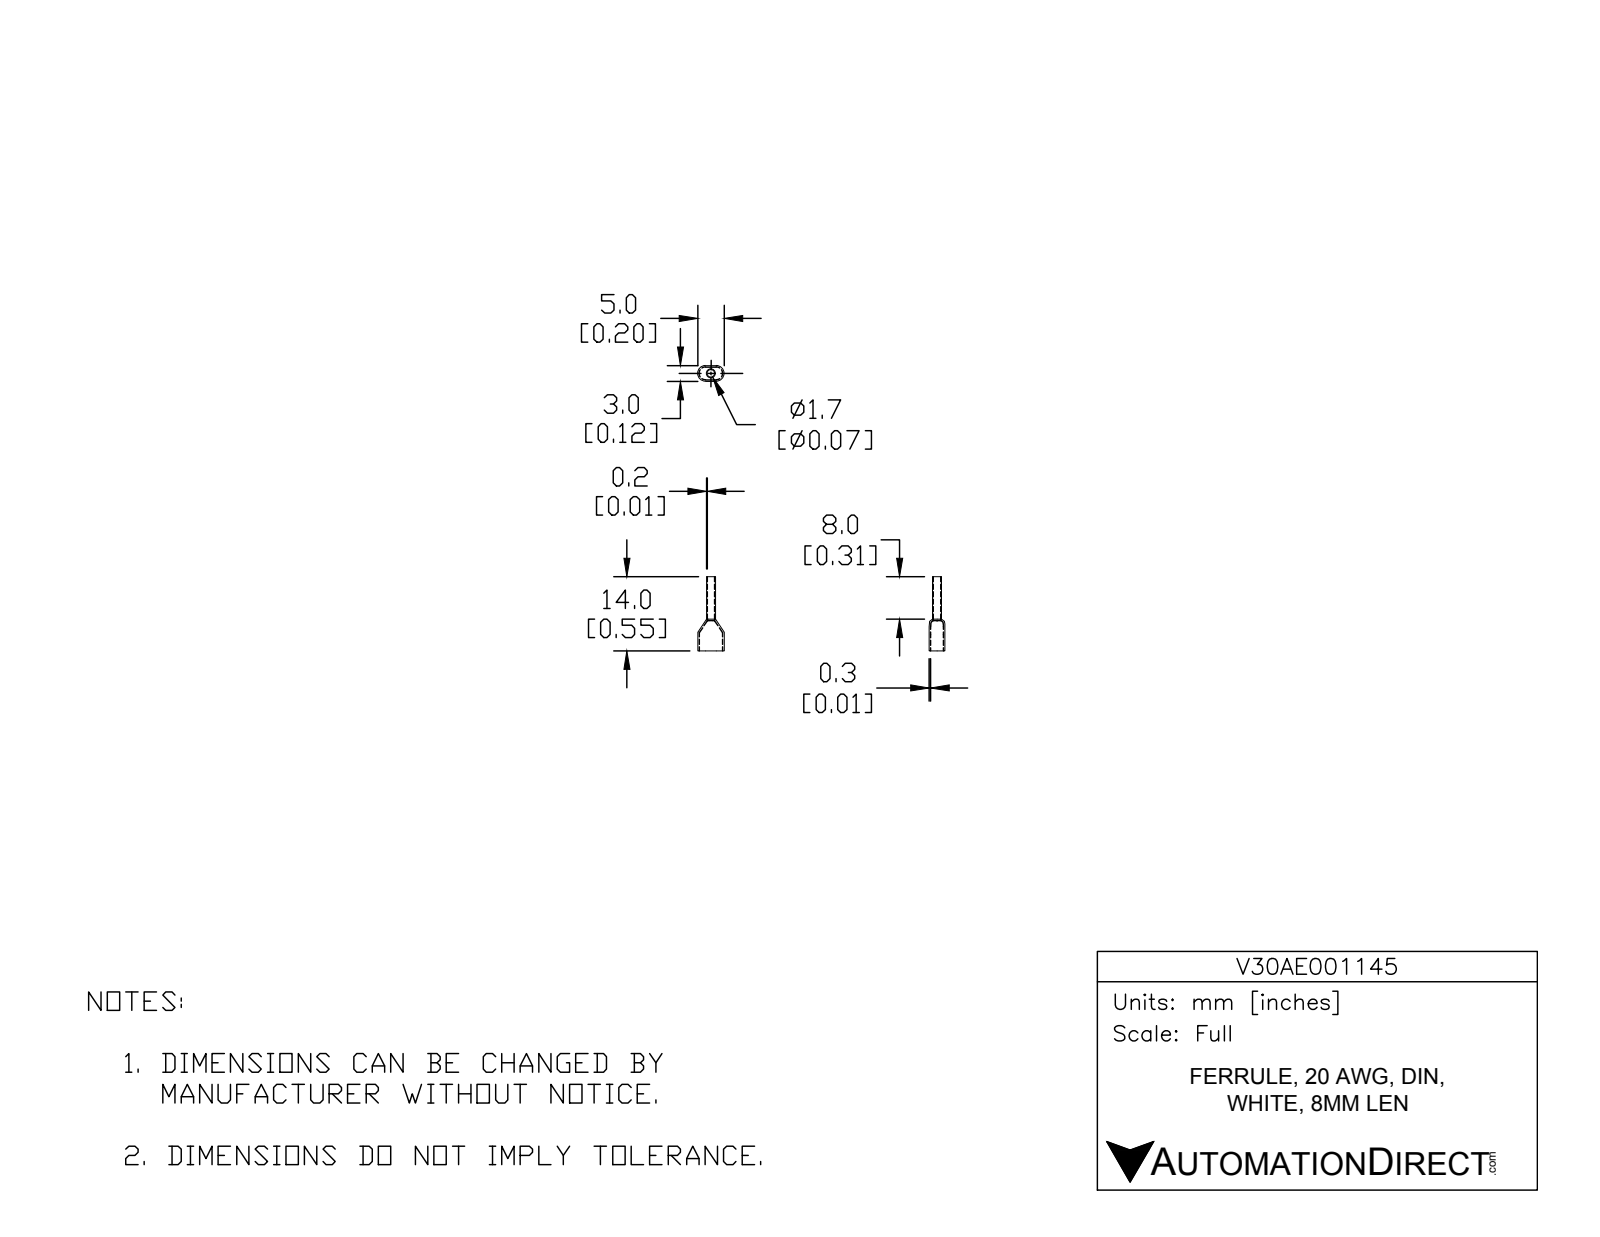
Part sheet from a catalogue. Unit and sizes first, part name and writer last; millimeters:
Units: millimetres
Overall size (bounding box): 14 × 5 × 3
Round holes (diameter × count): ⌀1.4 ×1
Round bosses / shafts (diameter × count): ⌀1.7 ×1
Partial cylindrical surfaces — rounded edges, fillets, slot ends (radius × count): R1.2 ×6, R1.5 ×6
Main face-to-face distances: 2.7, 3, 2.4, 6, 14, 8, 5.7, 8.3
Volume: 26 mm³ · Surface area: 220 mm²
Bodies: 2 solids, 36 faces (14 planar, 22 cylindrical, 0 other)
Part name (STEP PRODUCT): V30AE001145
STEP written by: SolidWorks 2017 (AUTOMOTIVE_DESIGN)
